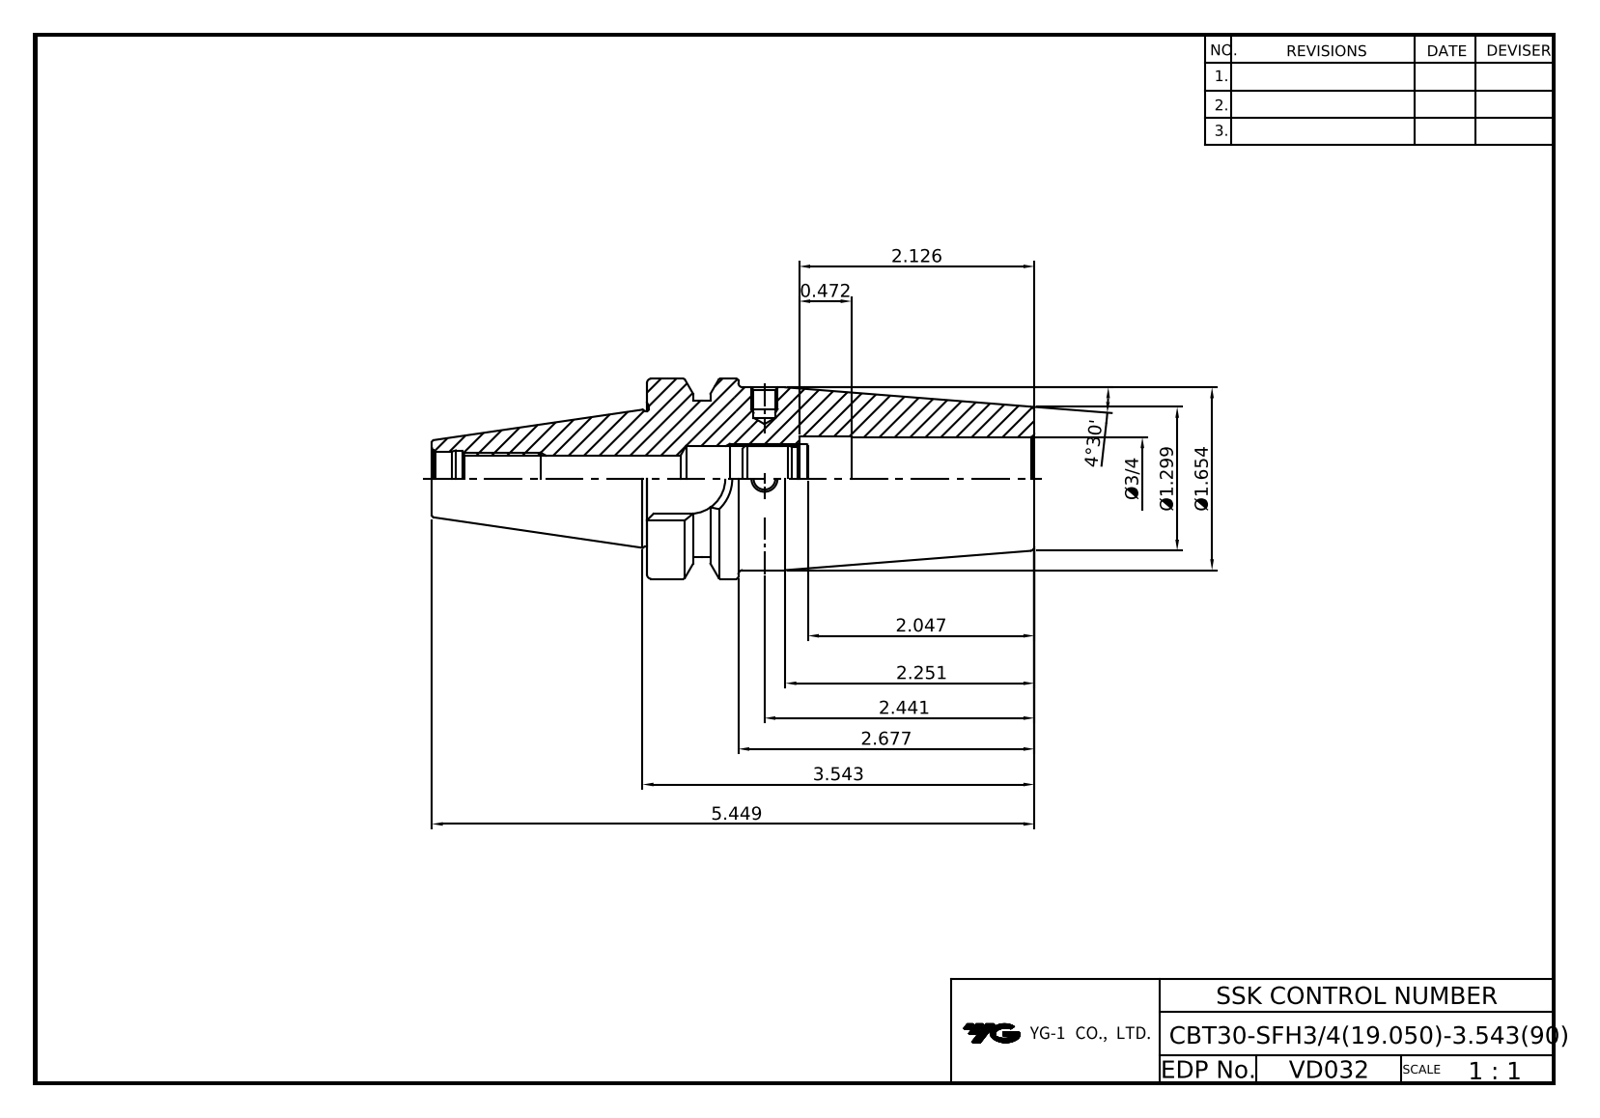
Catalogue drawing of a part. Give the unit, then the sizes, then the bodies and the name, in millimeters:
Units: millimetres
Overall size (bounding box): 138.4 × 46 × 46
Round holes (diameter × count): ⌀10 ×1, ⌀10.11 ×1, ⌀12.5 ×1, ⌀13.1 ×1, ⌀14.92 ×1, ⌀19.05 ×1, ⌀20.25 ×1
Round bosses / shafts (diameter × count): ⌀46 ×1, ⌀42 ×1, ⌀31.2 ×1
Partial cylindrical surfaces — rounded edges, fillets, slot ends (radius × count): R8.05 ×1, R18.8 ×1
Main face-to-face distances: 89, 32.6, 35, 54, 0.4, 34.6, 88.6, 16.1, 21, 20.6
Volume: 106 596 mm³ · Surface area: 24 001 mm²
Bodies: 1 solid, 62 faces (23 planar, 16 cylindrical, 23 other)
Part name (STEP PRODUCT): LO-CBT30-SFH19.05-90
STEP written by: Autodesk Inventor 2022 (AUTOMOTIVE_DESIGN)
